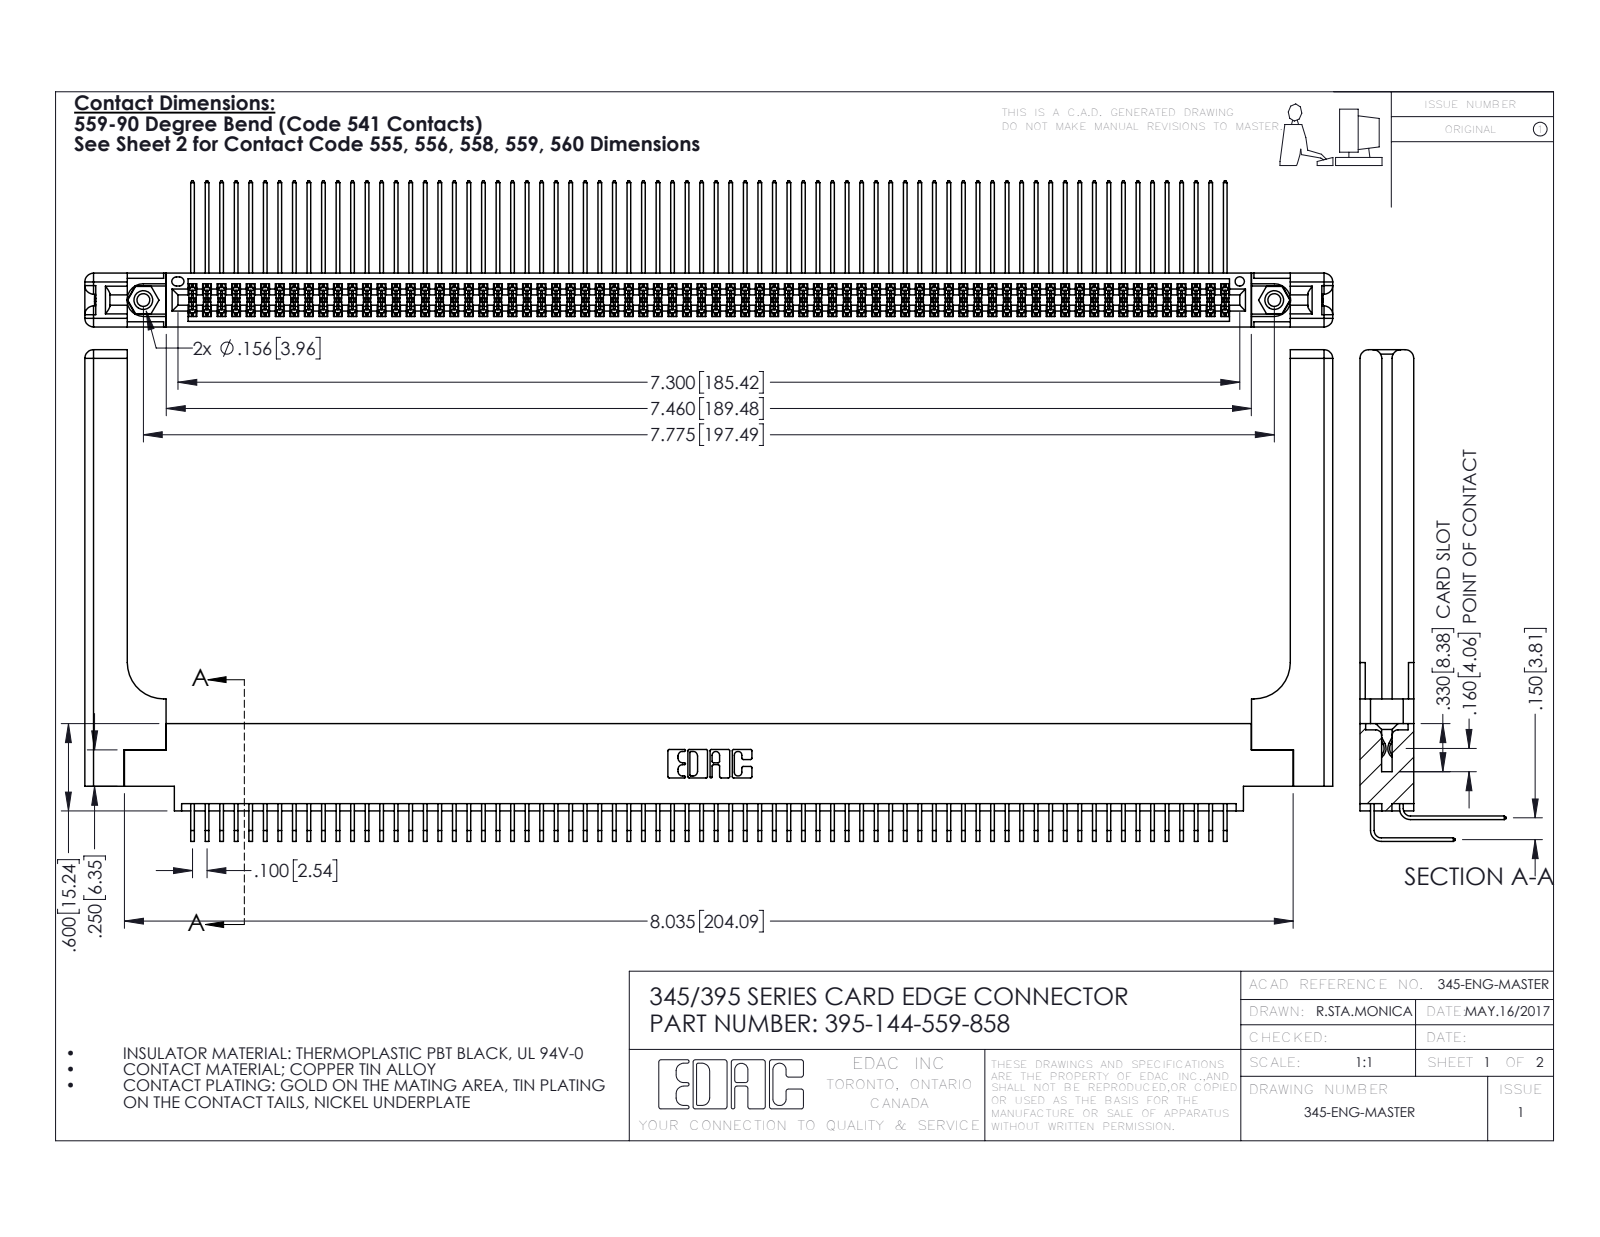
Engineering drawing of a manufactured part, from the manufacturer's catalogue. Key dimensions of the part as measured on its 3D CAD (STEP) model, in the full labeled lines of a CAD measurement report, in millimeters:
Part name (STEP PRODUCT): 345-292-001_558 559 Tail - 1; 345 Part_0.170 Offset - 0.156 Dia-TH; 395-144-559-858; 345-250-001_345-250-001-102 (+2 more)
STEP written by: SolidWorks 2016 (CONFIG_CONTROL_DESIGN)
Units: millimetres
Bodies: 149 solids, 7874 faces (5272 planar, 2542 cylindrical, 60 other)
Overall size (bounding box): 217.9 × 85.8 × 25.5
Volume: 30 640 mm³ · Surface area: 42 450 mm²
Round holes (diameter × count): ⌀2.3 ×2, ⌀3.2 ×2, ⌀4 ×2, ⌀1.6 ×1
Round bosses / shafts (diameter × count): ⌀3.9 ×2
Partial cylindrical surfaces — rounded edges, fillets, slot ends (radius × count): R0.2 ×217, R0.3 ×22, R1.5 ×16, R0.2 ×6, R0.8 ×6, R0.7 ×3, R0.4 ×2, R0.5 ×2
Main face-to-face distances: 1.8, 7.6, 9.4, 2.5, 6.9, 0.6, 5.1, 5.7, 4.4, 3.8
Hole centre spacings: 6.9, 191.5, 197.5
